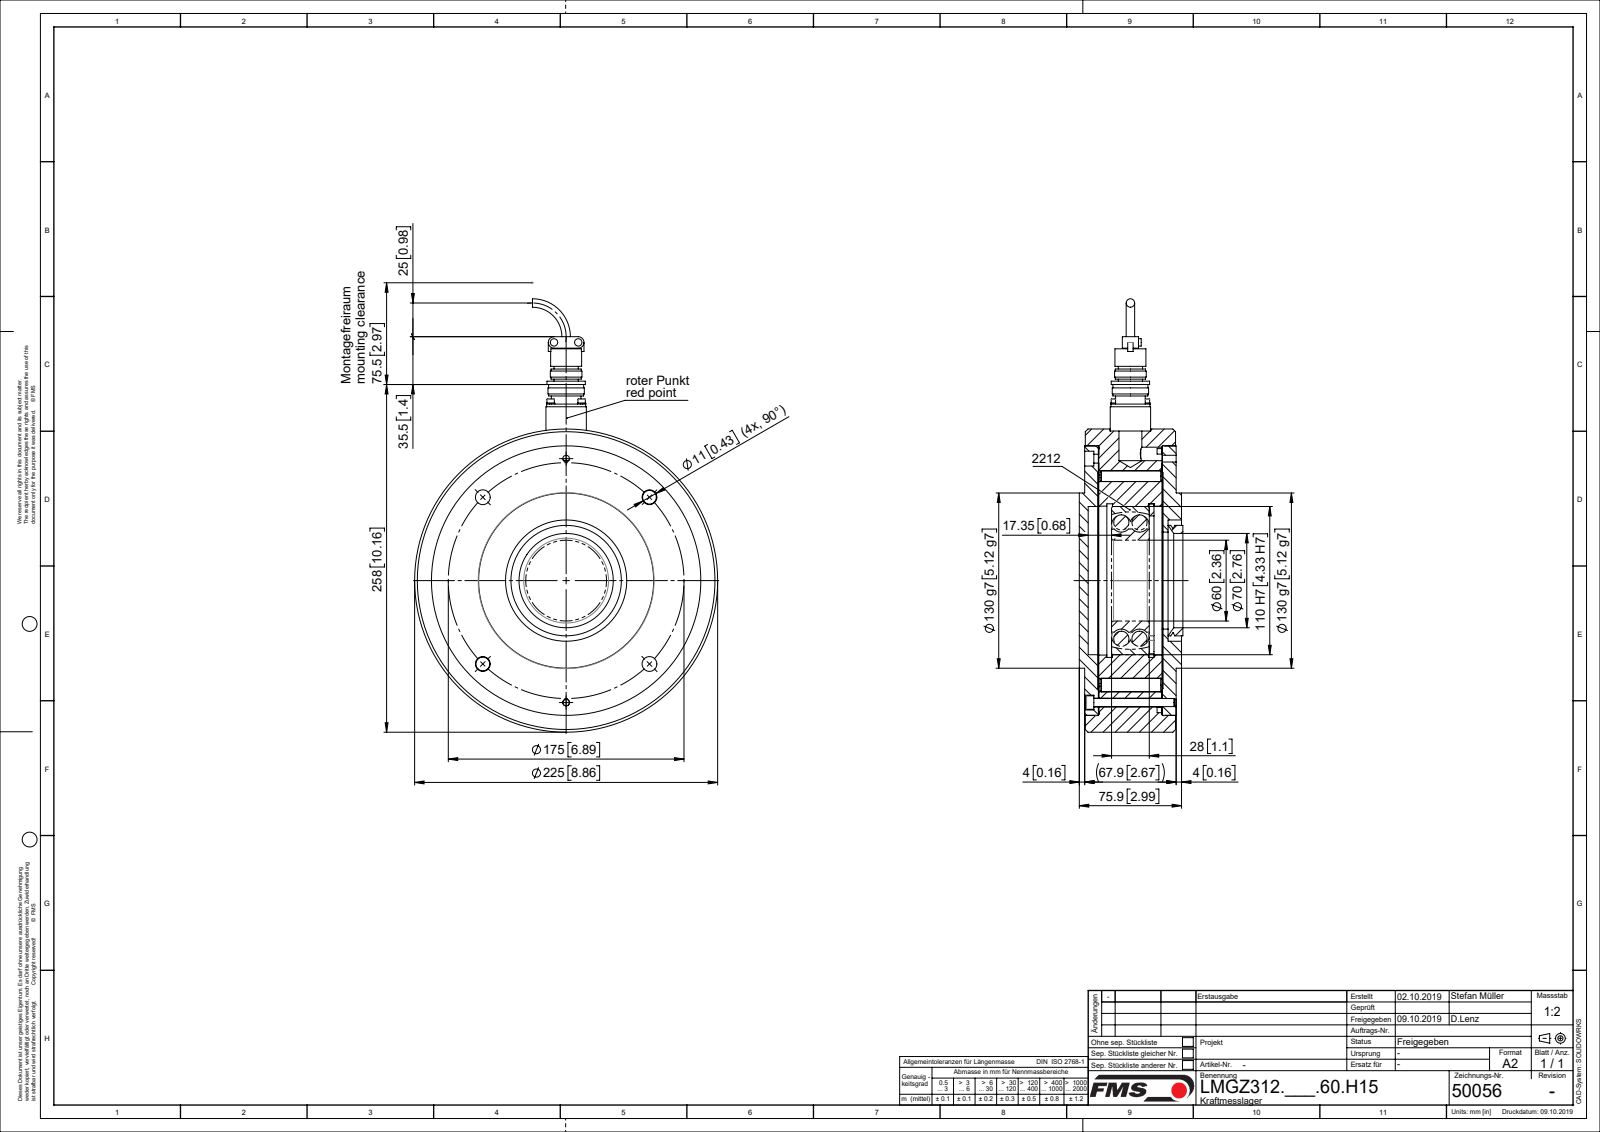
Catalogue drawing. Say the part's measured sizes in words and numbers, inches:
The part is named "L50056; L49151; TEIL1; L49026 (+8 more)". Its 3-D file was written by "Mechanical Desktop 2007 (CONFIG_CONTROL_DESIGN)". It is 19 solids with 385 faces: 109 planar, 226 cylindrical and 50 other. Overall it measures 12.663 by 8.858 by 3.028 inches. Its volume is 145.1 cubic inches and its surface area 603.6 square inches. Round holes: 6 of diameter 0.433, 4 of diameter 0.102, 4 of diameter 0.126, 4 of diameter 0.134, 4 of diameter 0.354, 2 of diameter 0.197, 2 of diameter 0.26, 1 of diameter 0.906, 1 of diameter 2.362, 1 of diameter 2.756, 1 of diameter 2.835, 1 of diameter 3.472. Round bosses or shafts: 6 of diameter 0.217, 4 of diameter 0.244, 4 of diameter 0.118, 4 of diameter 0.098, 1 of diameter 8.858, 1 of diameter 7.835, 1 of diameter 5.118, 1 of diameter 3.228. Partial cylindrical surfaces (rounded edges, fillets, slot ends): 2 of radius 0.167, 1 of radius 3.189, 1 of radius 3.386. The main face-to-face distances are 1.86, 0.411, 0.402, 2.262, 2.272, 1.87, 0.384, 0.02, 1.89, 0.382. The hole center spacings are 0.64, 0.906, 2.684, 3.445, 4.872, 6.474, 1.281, 3.563.
